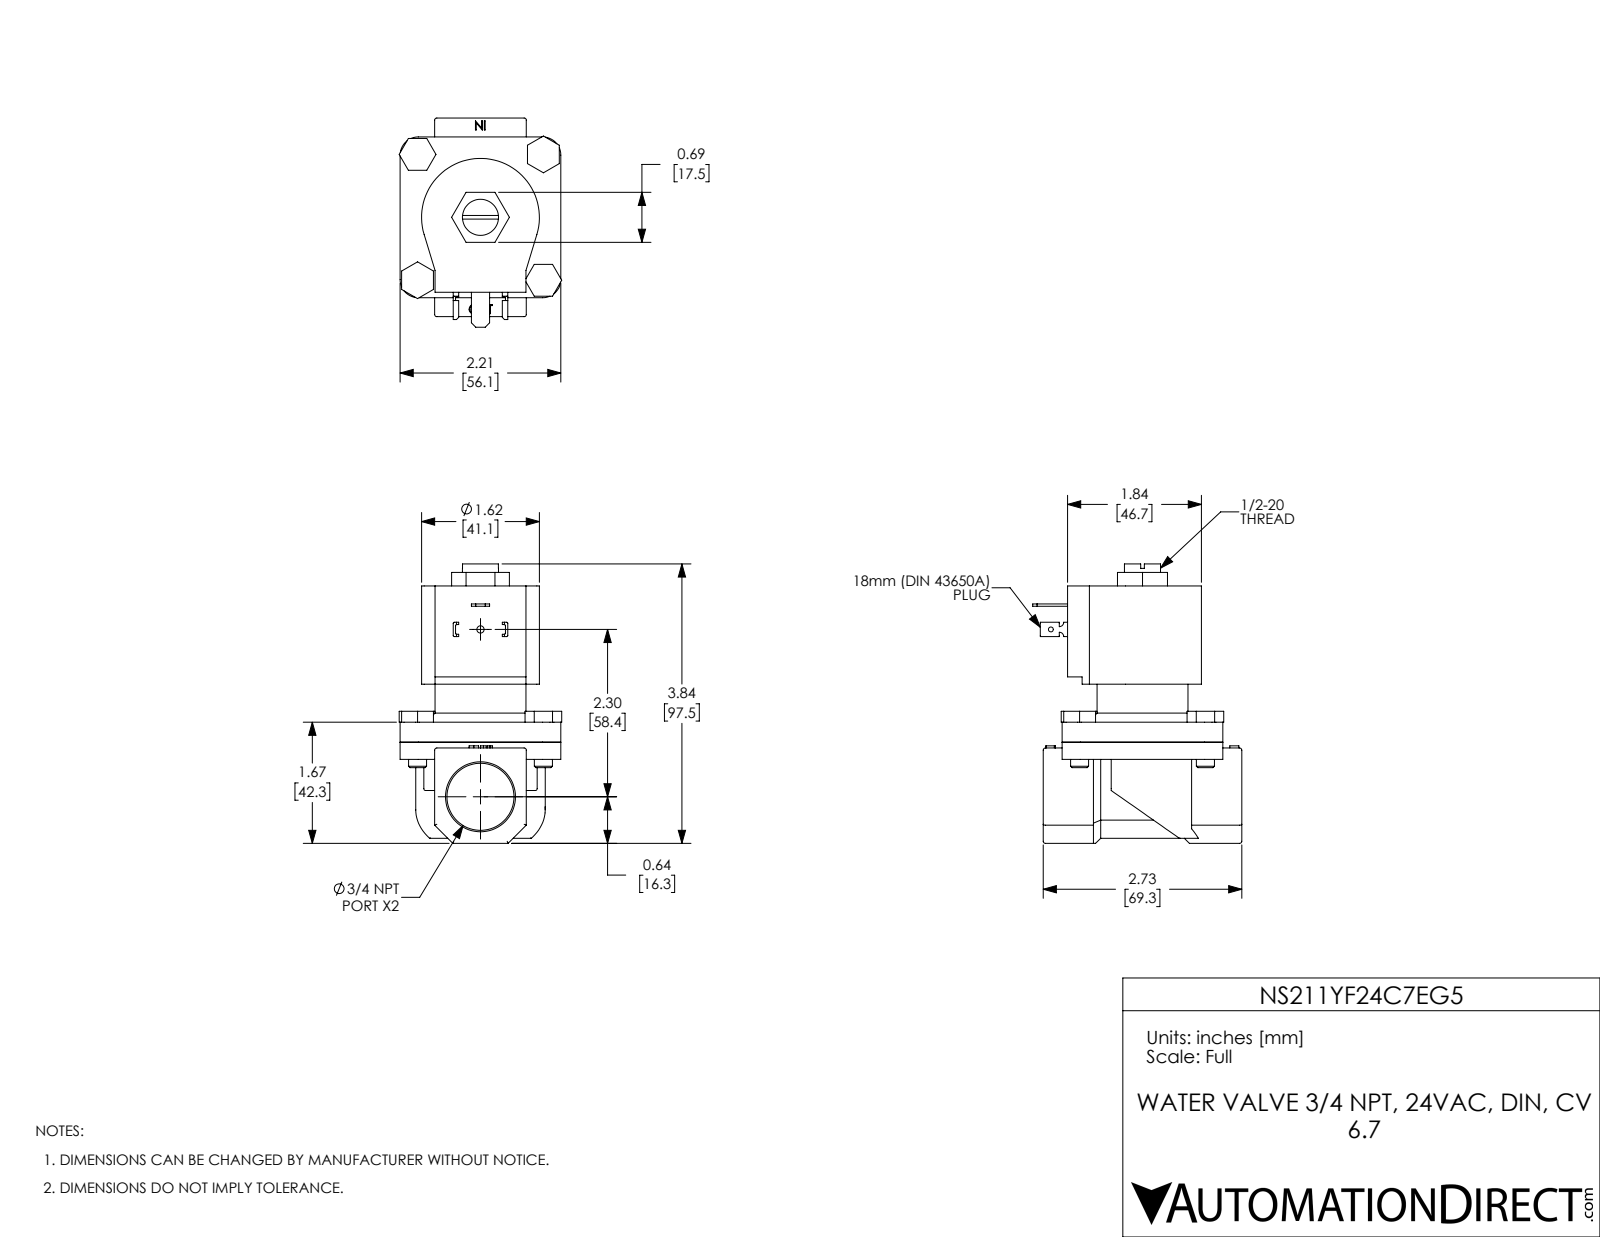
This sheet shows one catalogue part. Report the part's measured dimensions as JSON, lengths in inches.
{"part_name": "NS211YF24C7EG5", "step_written_by": "SolidWorks 2021 (CONFIG_CONTROL_DESIGN)", "units": "inches", "bodies": {"solids": 11, "faces": 332, "planar": 198, "cylindrical": 99, "other": 35}, "overall_size": [3.84, 2.875, 2.235], "volume_in3": 9.853, "surface_area_in2": 64.15, "round_holes": [[0.25, 4], [0.067, 1], [0.1, 1], [0.496, 1], [0.512, 1], [0.922, 1], [1.155, 1]], "round_bosses_or_shafts": [[0.248, 4], [1.25, 1]], "partial_cylinders_radius": [[0.03, 15], [0.015, 8], [0.25, 4], [0.06, 2], [0.81, 1], [0.89, 1]], "face_to_face_distances": [0.275, 2.148, 1.873, 0.475, 1.735, 2.21, 0.798, 0.523, 1.35, 0.236], "hole_center_spacings": [1.223, 1.73, 2.446, 2.3]}
